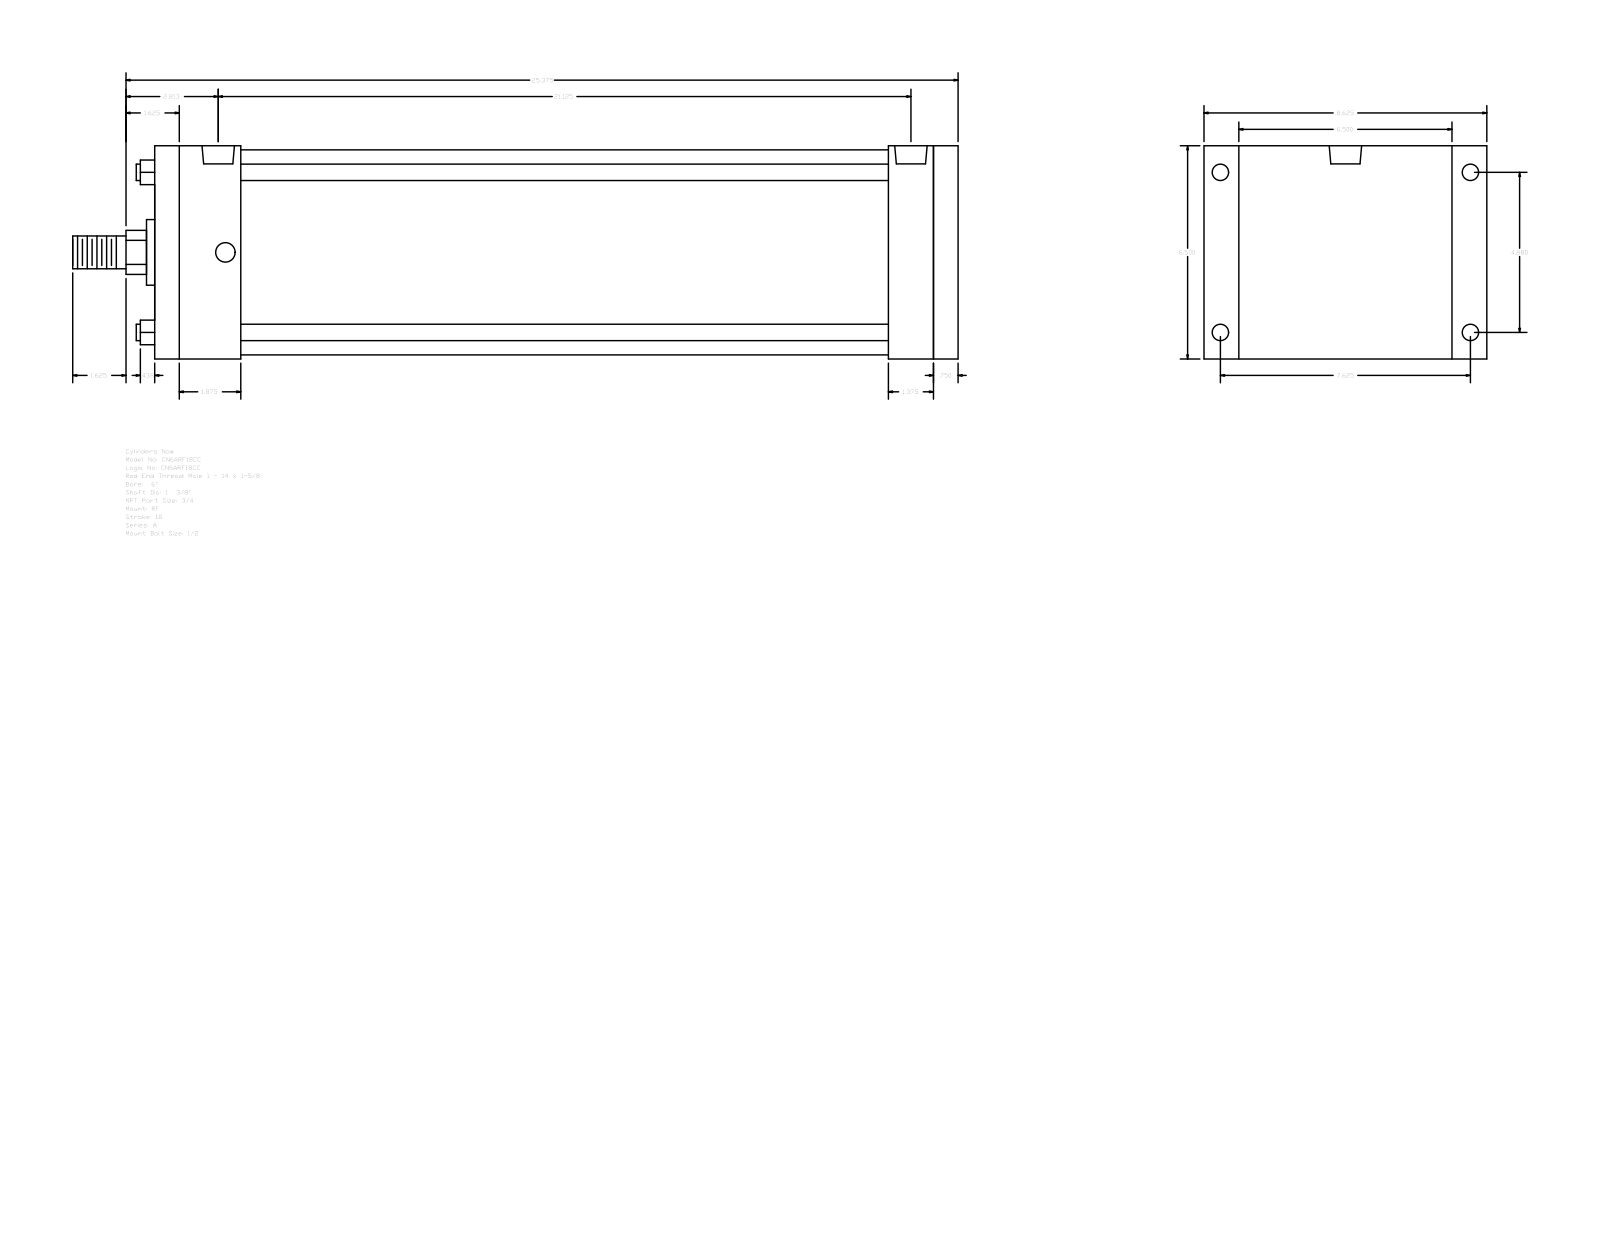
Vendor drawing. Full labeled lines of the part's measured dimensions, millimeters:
Part name (STEP PRODUCT): A_RF__0600_1.375
STEP written by: GSSL Pune (CONFIG_CONTROL_DESIGN)
Units: millimetres
Bodies: 0 solids, 92 faces (64 planar, 28 cylindrical, 0 other)
Overall size (bounding box): 685.8 × 219.07 × 165.1
Round holes (diameter × count): ⌀12.7 ×4, ⌀15.08 ×4, ⌀25.12 ×2
Round bosses / shafts (diameter × count): ⌀12.7 ×4, ⌀158.75 ×1, ⌀50.8 ×1, ⌀34.92 ×1, ⌀25.4 ×1
Partial cylindrical surfaces — rounded edges, fillets, slot ends (radius × count): R17.06 ×1
Main face-to-face distances: 165.1, 622.29, 603.25, 19.04, 53.97, 66.67, 536.58, 555.62, 568.32, 501.65
Hole centre spacings: 5.56, 123.96, 193.68, 229.95, 525.45, 531.01, 536.57
